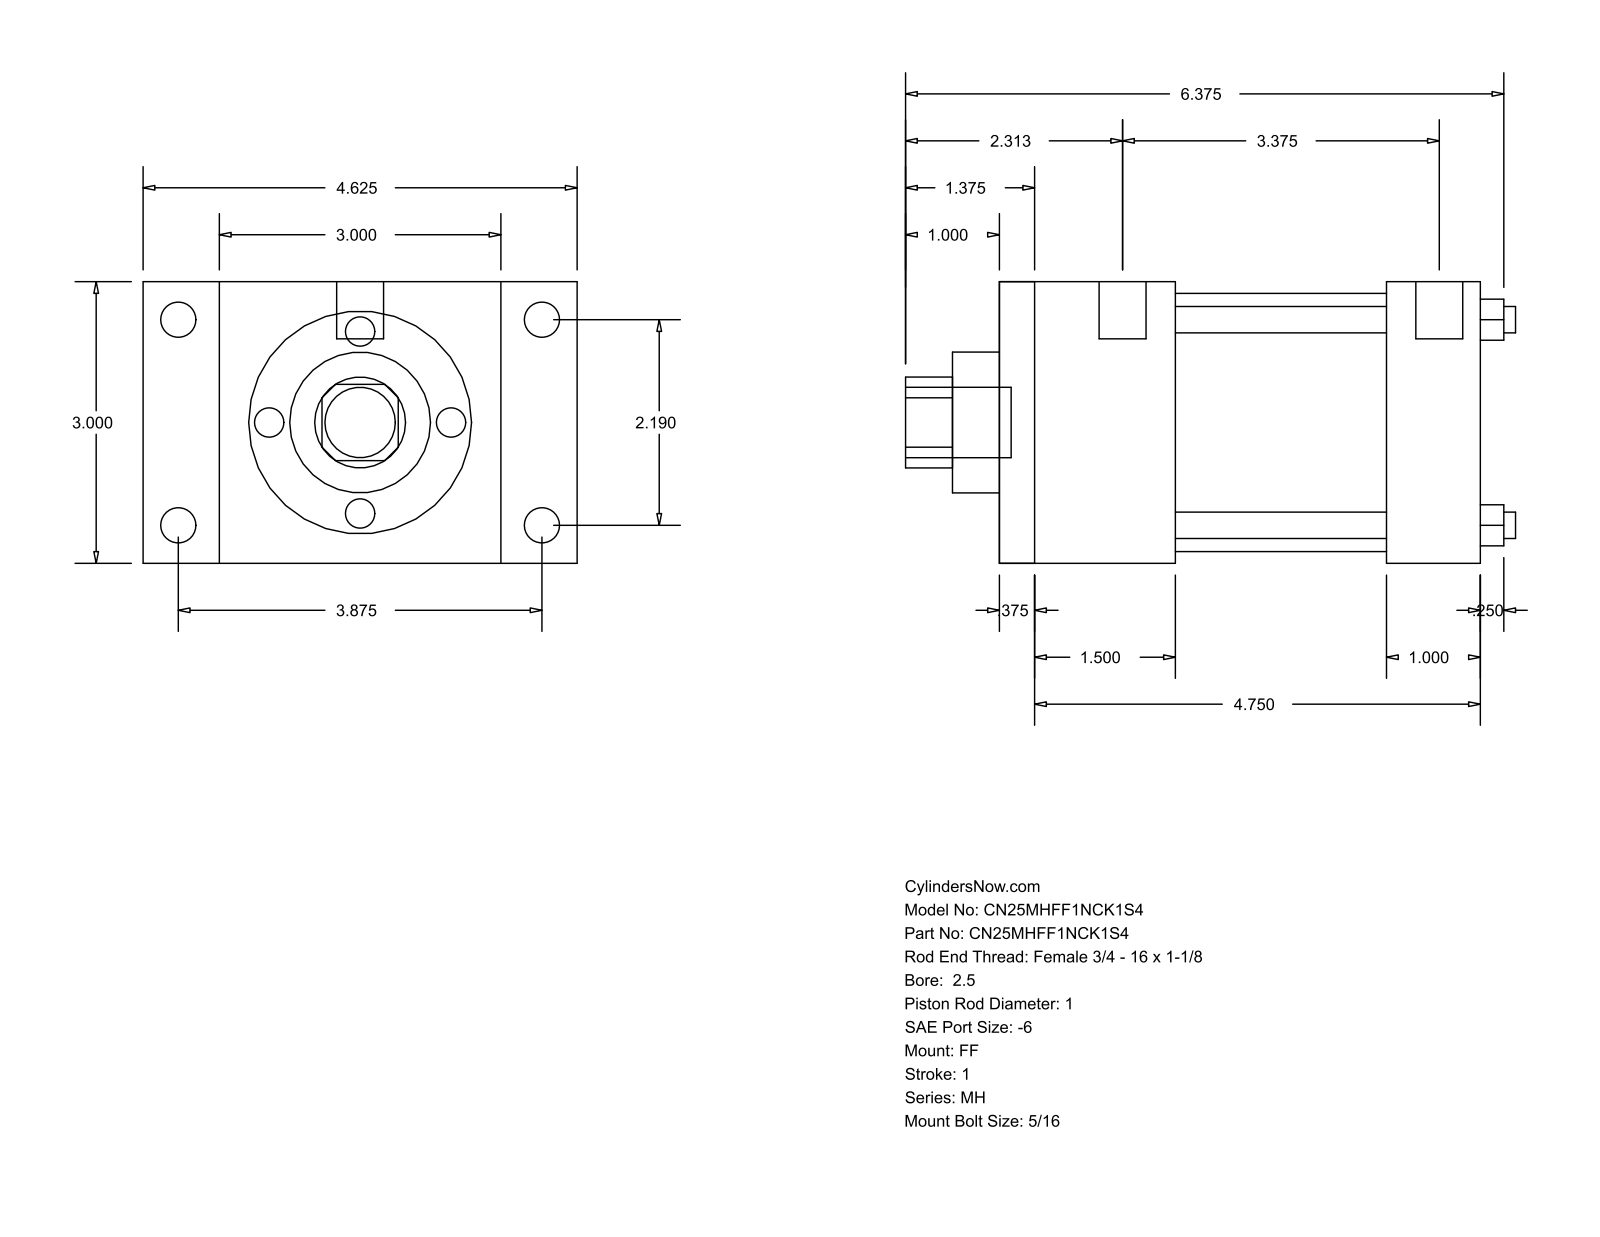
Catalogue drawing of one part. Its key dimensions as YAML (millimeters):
part_name: "MH_FF__0250_1"
step_written_by: "GSSL Pune (CONFIG_CONTROL_DESIGN)"
units: millimeters
bodies: {solids: 0, faces: 92, planar: 64, cylindrical: 28, other: 0}
overall_size: [165.1, 117.47, 76.2]
round_holes:
  - {diameter: 7.14, count: 4}
  - {diameter: 25.4, count: 1}
  - {diameter: 38.1, count: 1}
  - {diameter: 69.85, count: 1}
round_bosses_or_shafts:
  - {diameter: 9.53, count: 4}
  - {diameter: 5.56, count: 4}
  - {diameter: 12.7, count: 2}
  - {diameter: 19.05, count: 1}
partial_cylinders:
  - {radius: 12.29, count: 1}
face_to_face_distances: [76.2, 130.17, 120.65, 9.52, 25.39, 47.63, 104.78, 38.11, 95.26, 57.15]
hole_center_spacings: [39.33, 55.62, 78.66]
